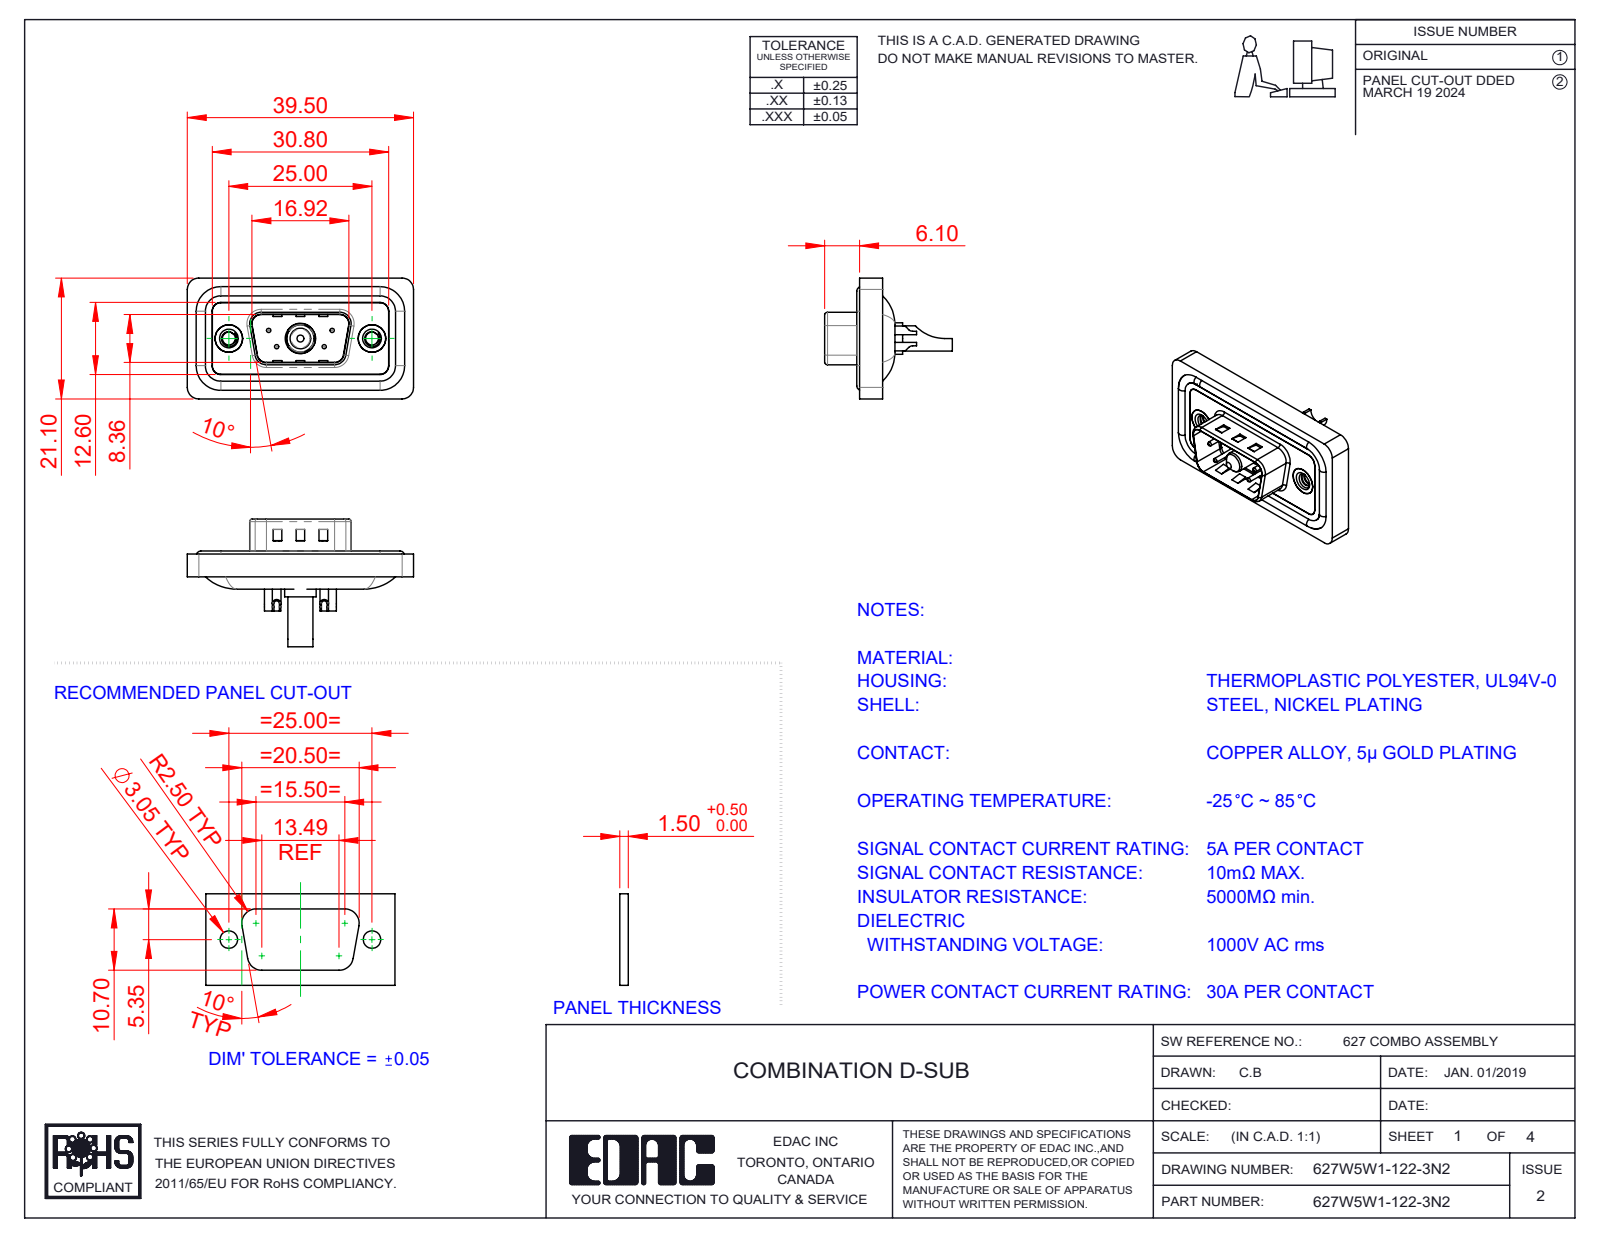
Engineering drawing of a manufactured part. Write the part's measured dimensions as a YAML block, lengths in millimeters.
part_name: "627Combo Threaded Rivet_2; 627Combo Waterproof Housing_09 Contacts; 627Combo Contact Row 1_22; 627Combo Shell Rear_09 Contacts (+5 more)"
step_written_by: "SolidWorks 2023 (CONFIG_CONTROL_DESIGN)"
units: millimeters
bodies: {solids: 13, faces: 604, planar: 194, cylindrical: 266, other: 144}
overall_size: [39.5, 22.3, 21.1]
volume: 4418
surface_area: 7081
round_holes:
  - {diameter: 0.75, count: 4}
  - {diameter: 1, count: 4}
  - {diameter: 1.6, count: 4}
  - {diameter: 2, count: 4}
  - {diameter: 2.26, count: 2}
  - {diameter: 4, count: 2}
  - {diameter: 4.8, count: 2}
  - {diameter: 5, count: 2}
  - {diameter: 3.5, count: 1}
  - {diameter: 4.85, count: 1}
  - {diameter: 5.3, count: 1}
round_bosses_or_shafts:
  - {diameter: 1.6, count: 4}
  - {diameter: 1.5, count: 4}
  - {diameter: 4.9, count: 2}
  - {diameter: 5.5, count: 1}
  - {diameter: 5.2, count: 1}
  - {diameter: 4.75, count: 1}
  - {diameter: 4.4, count: 1}
  - {diameter: 3.75, count: 1}
partial_cylinders:
  - {radius: 1.5, count: 22}
  - {radius: 2, count: 18}
  - {radius: 0.5, count: 8}
  - {radius: 1.6, count: 8}
  - {radius: 1, count: 6}
  - {radius: 0.25, count: 4}
  - {radius: 0.6, count: 4}
  - {radius: 0.65, count: 4}
face_to_face_distances: [0.4, 1.1, 2.9, 1.6, 3.1, 0.5, 1.5, 2.5, 4, 0.8]
hole_center_spacings: [3.16, 5.72, 7.1, 12.5, 18.1, 4.39, 4.4, 8.31]
